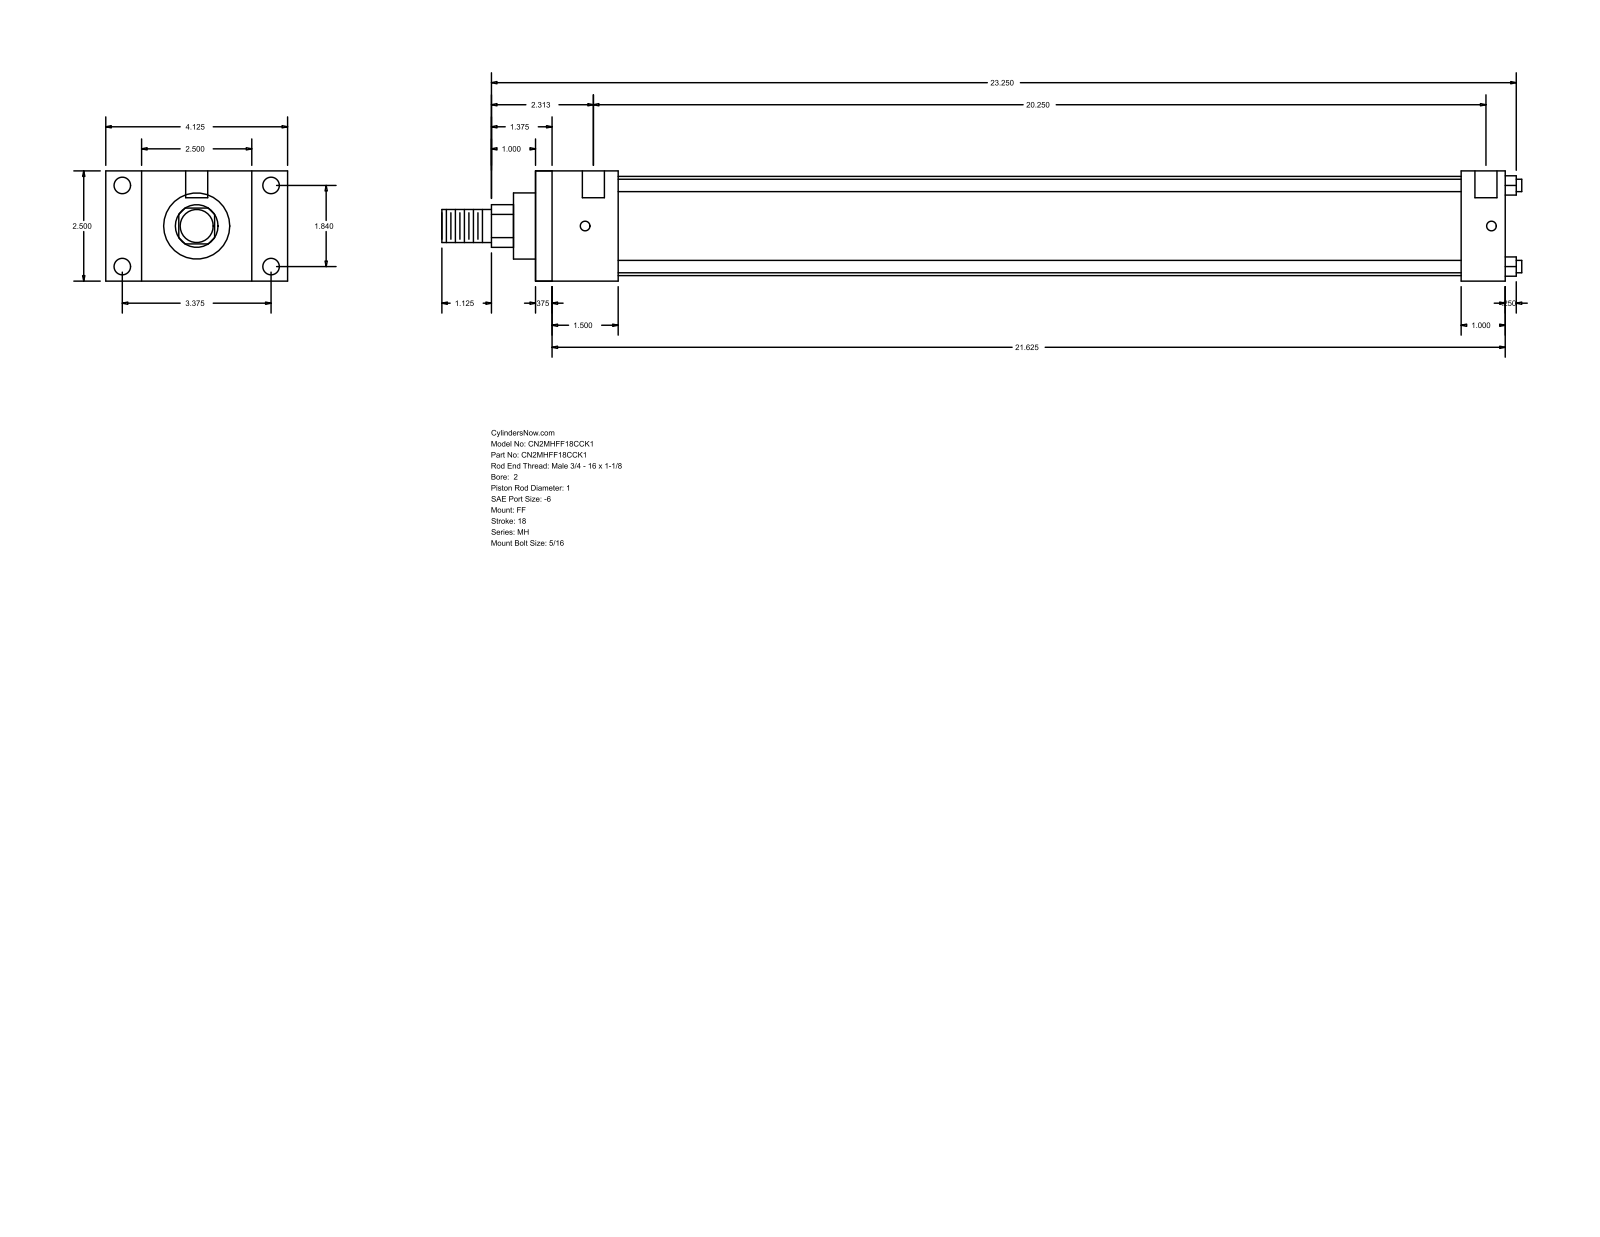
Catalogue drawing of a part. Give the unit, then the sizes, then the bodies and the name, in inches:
Units: inches
Overall size (bounding box): 24.5 × 4.125 × 2.5
Round holes (diameter × count): ⌀0.219 ×4, ⌀0.375 ×4, ⌀0.5 ×2
Round bosses / shafts (diameter × count): ⌀0.281 ×4, ⌀2.25 ×1, ⌀1.5 ×1, ⌀1 ×1, ⌀0.75 ×1
Partial cylindrical surfaces — rounded edges, fillets, slot ends (radius × count): R0.484 ×1
Main face-to-face distances: 2.5, 22, 0.375, 21.625, 0.813, 1, 1.875, 21, 1.5, 20.625
Hole centre spacings: 1.84, 3.375, 3.844, 20.562, 0.125, 0.187, 20.25, 20.375
Bodies: 0 solids, 92 faces (64 planar, 28 cylindrical, 0 other)
Part name (STEP PRODUCT): MH_FF__0200_1
STEP written by: GSSL Pune (CONFIG_CONTROL_DESIGN)
